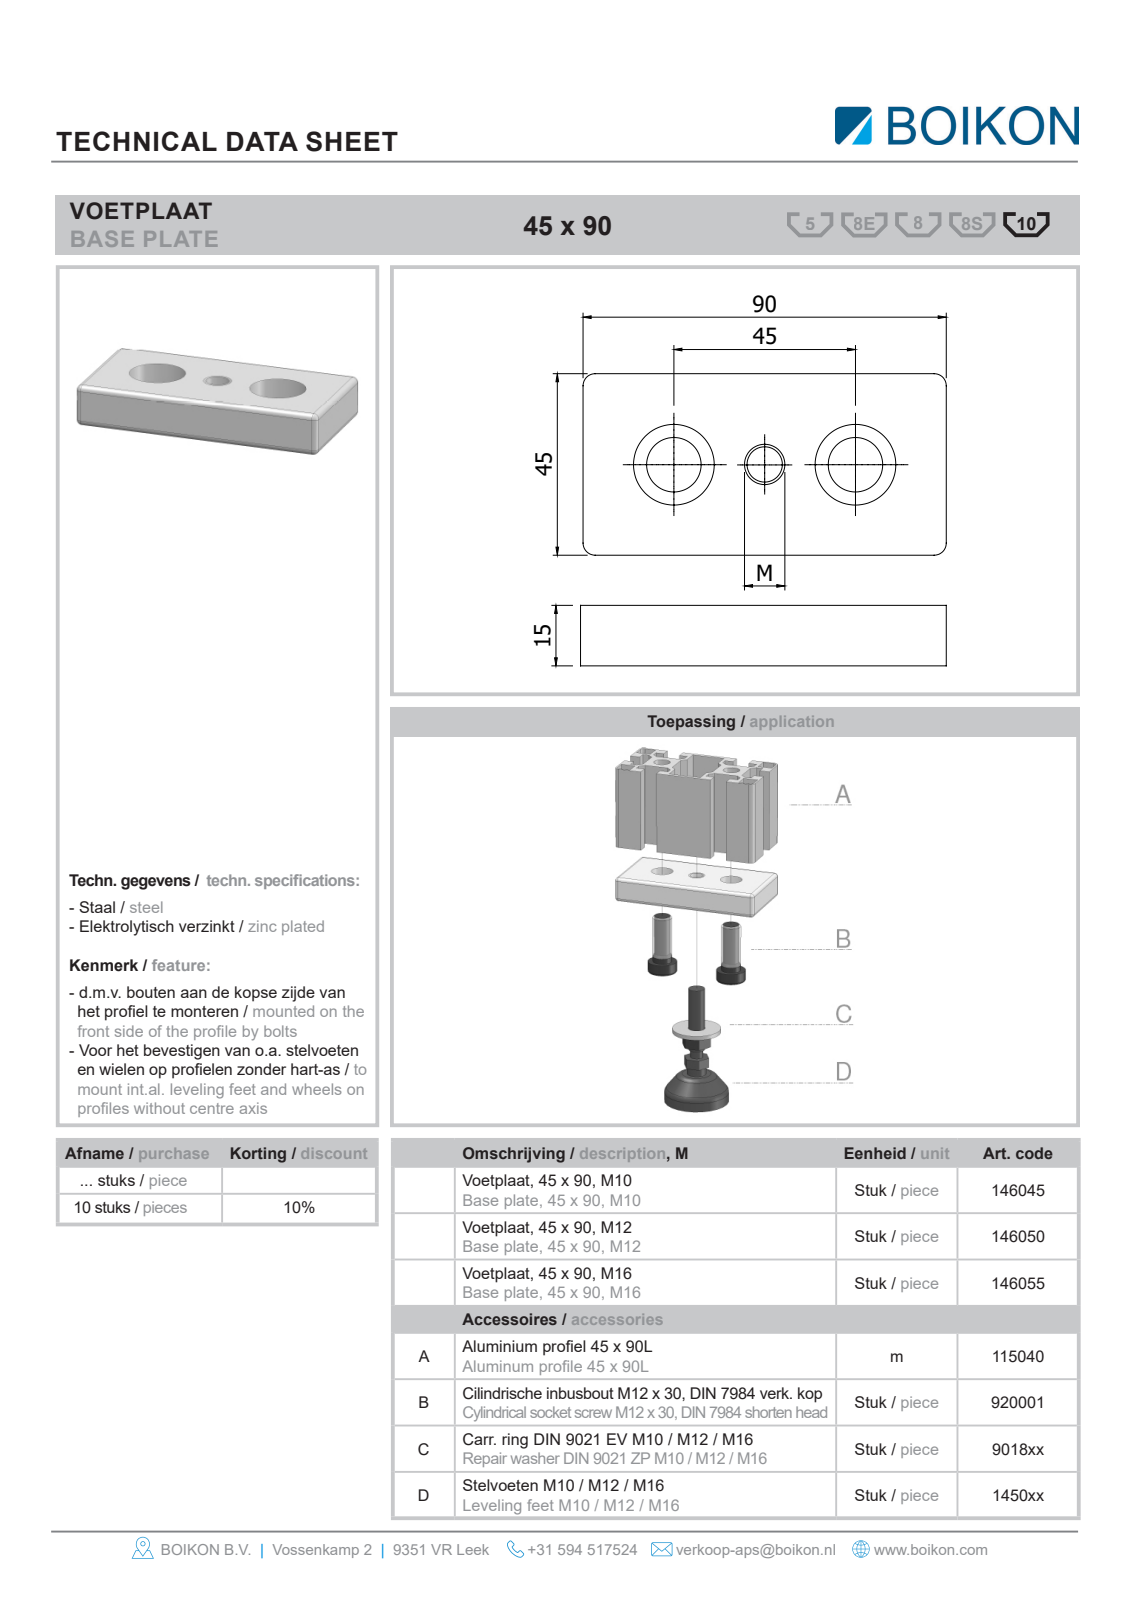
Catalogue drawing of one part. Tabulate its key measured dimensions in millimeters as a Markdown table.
| quantity | value |
| --- | --- |
| part name | Root; 146055Voetplaat 45x90 M16BOIKON; 920001Cil. inb. M12 x 30, DIN 7984 verk. kopBOIKON0 |
| STEP written by | HiCAD 2013 1802.4 Build 509 (AUTOMOTIVE_DESIGN) |
| units | millimeters |
| bodies | 3 solids, 57 faces (40 planar, 11 cylindrical, 6 other) |
| overall size | 90 × 45 × 38.2 |
| volume | 58 419 mm³ |
| surface area | 17 439 mm² |
| round holes (diameter × count) | 13.5 × 2, 20 × 2, 16 × 1 |
| round bosses / shafts (diameter × count) | 18 × 2, 12 × 2, 9.85 × 2 |
| main face-to-face distances | 15, 45, 90, 6.8, 8.2, 13.8, 7, 1.2, 37, 23.2 |
| hole center spacings | 22.5, 45 |
